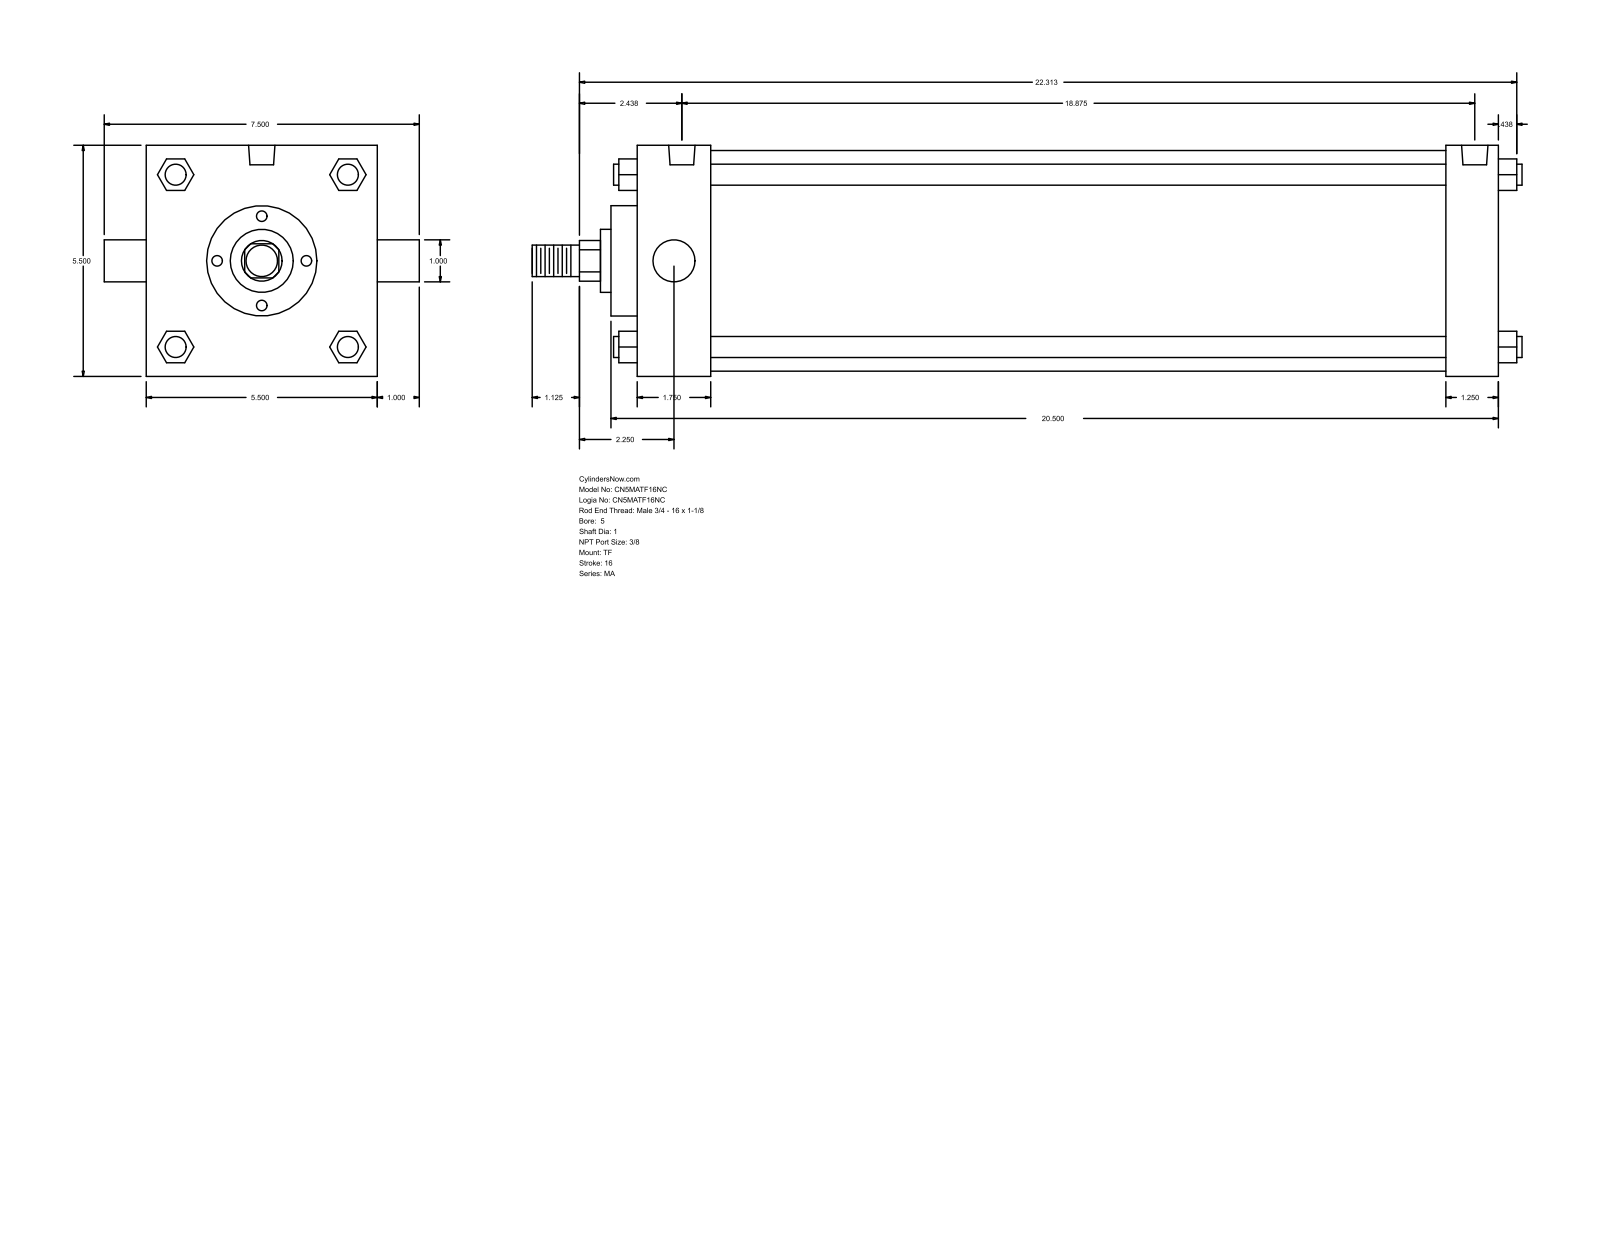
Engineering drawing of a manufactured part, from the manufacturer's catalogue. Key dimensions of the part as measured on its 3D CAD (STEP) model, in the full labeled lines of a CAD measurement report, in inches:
Part name (STEP PRODUCT): MA_TF__0500_1
STEP written by: GSSL Pune (CONFIG_CONTROL_DESIGN)
Units: inches
Bodies: 0 solids, 122 faces (93 planar, 29 cylindrical, 0 other)
Overall size (bounding box): 23.563 × 7.5 × 5.5
Round holes (diameter × count): ⌀0.437 ×3, ⌀0.627 ×2
Round bosses / shafts (diameter × count): ⌀0.5 ×4, ⌀1 ×2, ⌀5.25 ×1, ⌀2.625 ×1, ⌀1.5 ×1, ⌀0.75 ×1
Partial cylindrical surfaces — rounded edges, fillets, slot ends (radius × count): R0.484 ×1
Main face-to-face distances: 5.5, 20.5, 19.25, 1.25, 1.75, 17.5, 18.75, 0.625, 2.375, 19.875
Hole centre spacings: 0.187, 18.688, 18.5, 18.875
